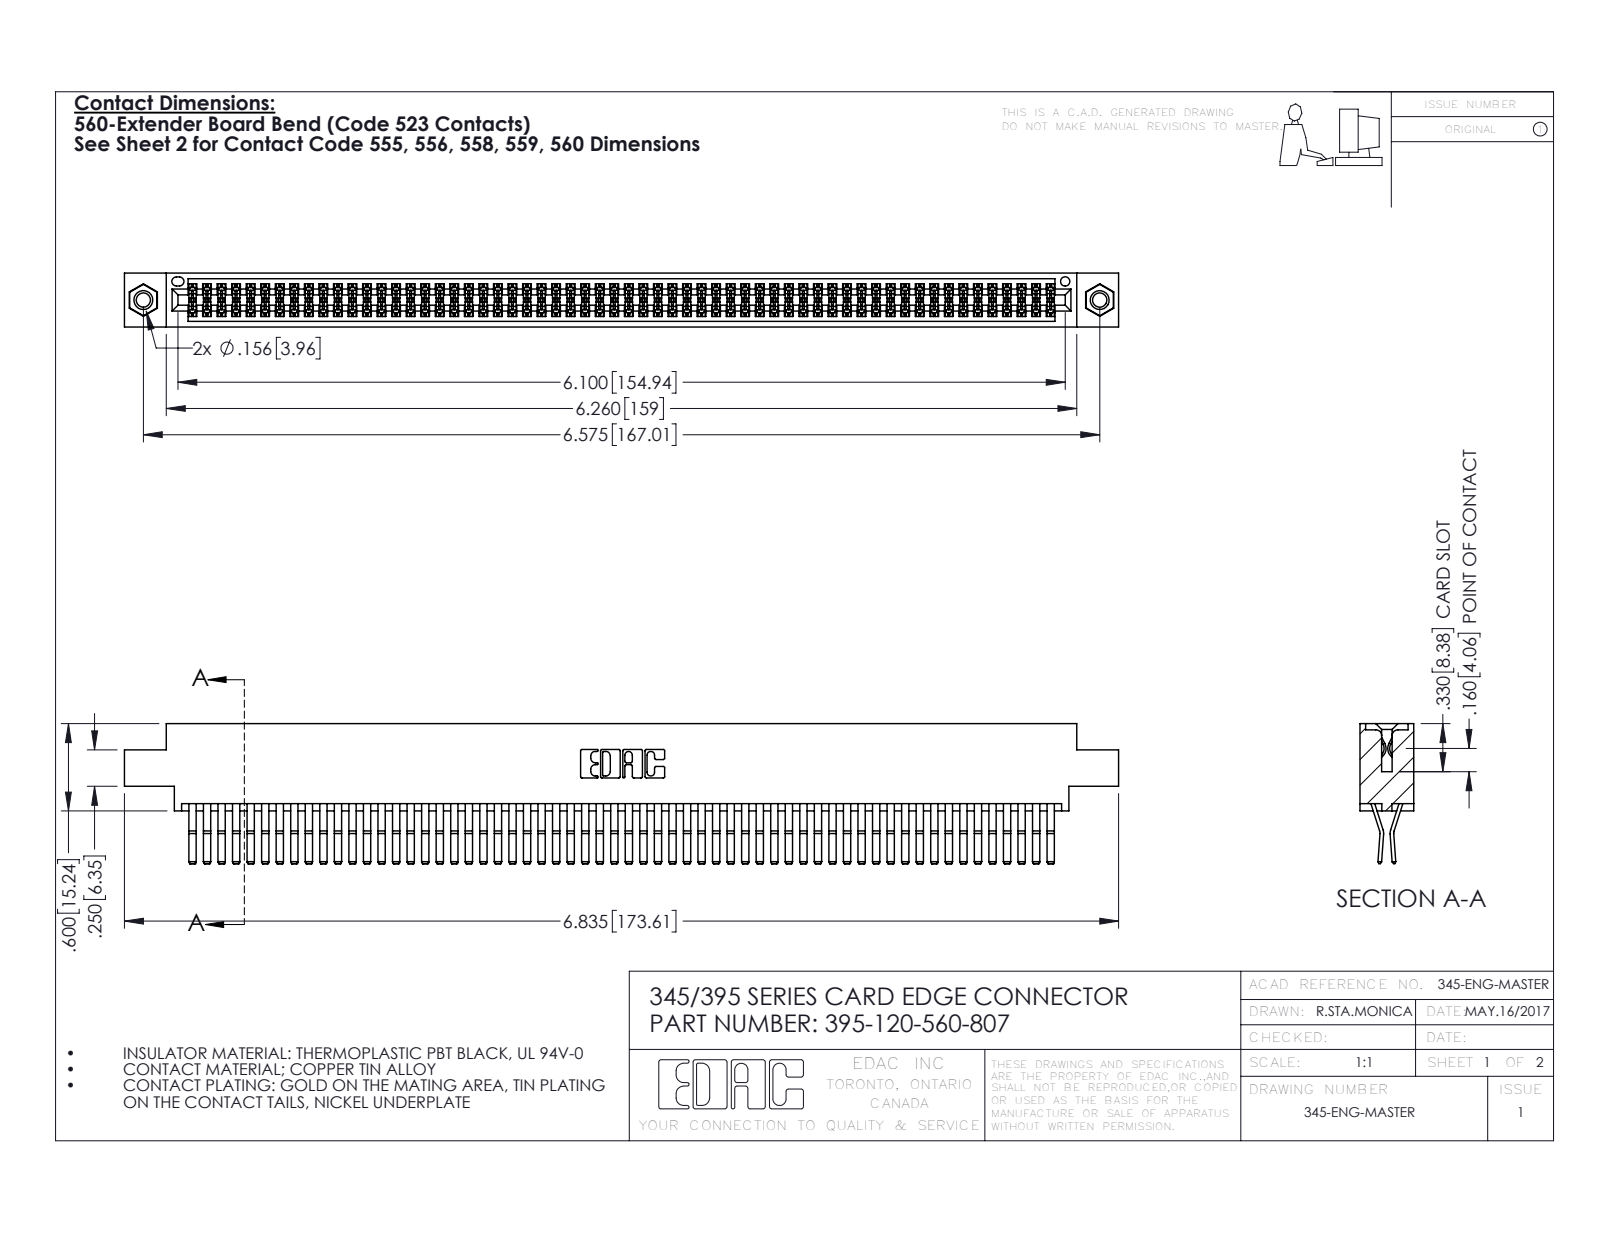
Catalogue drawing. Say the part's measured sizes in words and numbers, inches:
The part is named "345 Part_0.170 Offset - 0.156 Dia-TI; 395-120-560-807; 345-292-001_560 Tail; 345-250-001_345-250-005-103". Its 3-D file was written by "SolidWorks 2016 (CONFIG_CONTROL_DESIGN)". It is 123 solids with 6430 faces: 4076 planar, 2338 cylindrical and 16 other. Overall it measures 6.835 by 0.962 by 0.37 inches. Its volume is 1.08 cubic inches and its surface area 44.48 square inches. Round holes: 2 of diameter 0.098, 2 of diameter 0.125, 2 of diameter 0.156, 1 of diameter 0.064. Round bosses or shafts: 2 of diameter 0.155. Partial cylindrical surfaces (rounded edges, fillets, slot ends): 181 of radius 0.006, 22 of radius 0.01, 6 of radius 0.007, 6 of radius 0.031, 3 of radius 0.026, 2 of radius 0.01, 2 of radius 0.014, 2 of radius 0.019. The main face-to-face distances are 0.025, 0.072, 0.298, 0.37, 0.2, 0.098, 0.272, 0.225, 0.175, 0.149. The hole center spacings are 0.27, 6.339, 6.575.
